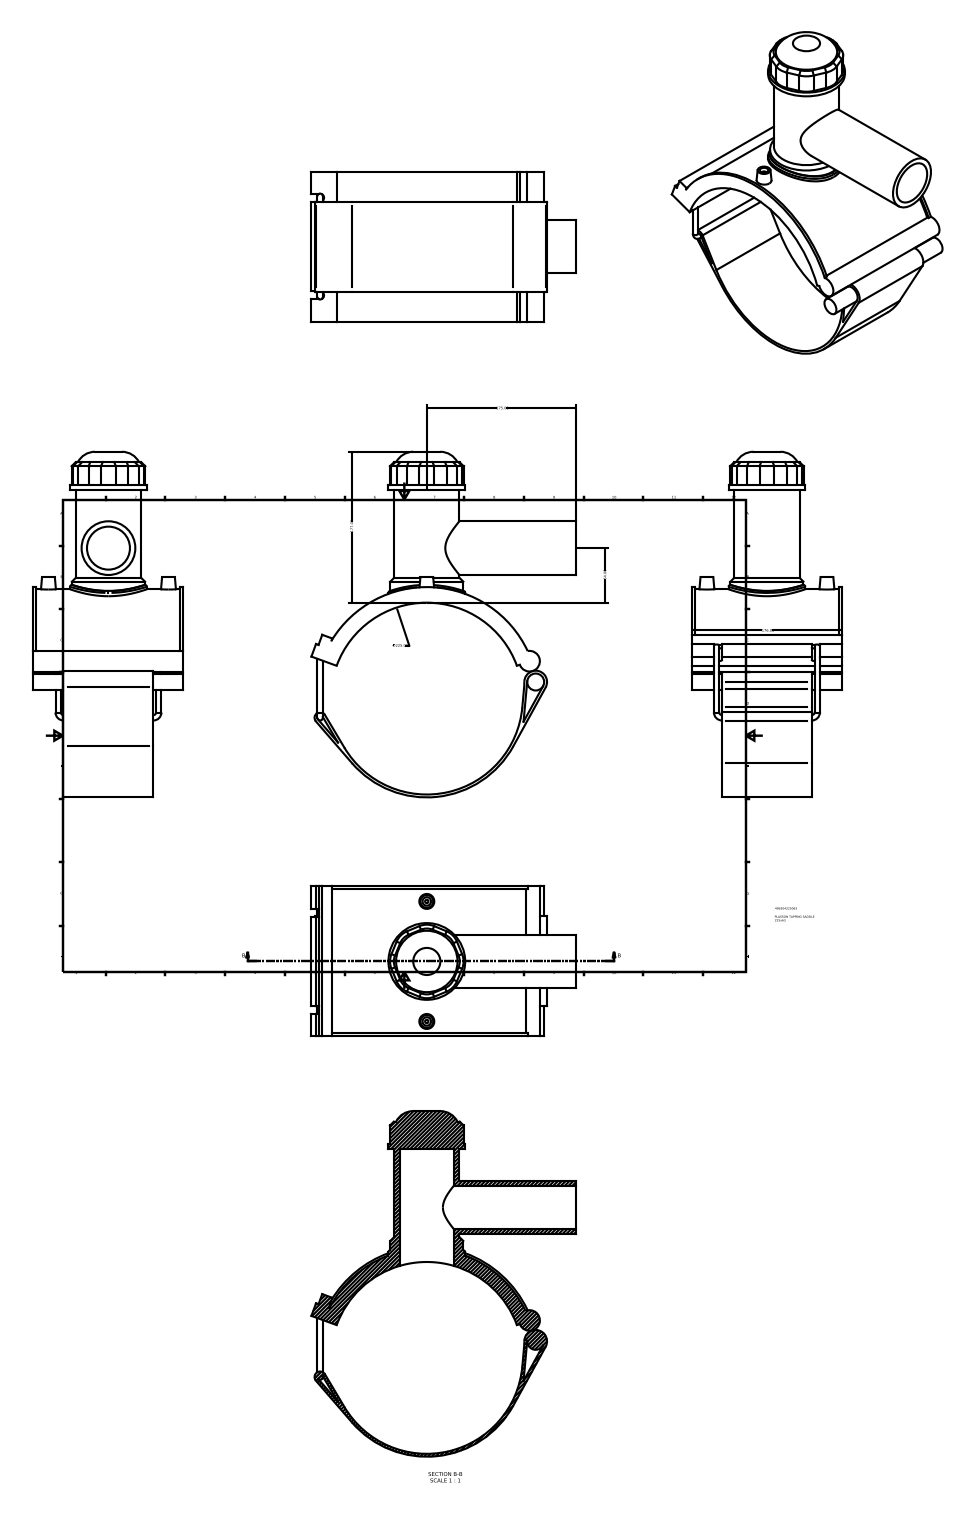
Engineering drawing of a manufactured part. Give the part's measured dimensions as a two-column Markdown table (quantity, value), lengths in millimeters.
| quantity | value |
| --- | --- |
| part name | 496304225063 |
| STEP written by | Autodesk Inventor 2015 (AUTOMOTIVE_DESIGN) |
| units | millimeters |
| bodies | 1 solid, 121 faces (68 planar, 38 cylindrical, 15 other) |
| overall size | 405.38 × 310.32 × 176 |
| volume | 1 714 000 mm³ |
| surface area | 374 360 mm² |
| round holes (diameter × count) | 10 × 2, 50.4 × 1, 63 × 1 |
| round bosses / shafts (diameter × count) | 6.3 × 2, 4 × 2, 90 × 1, 85.5 × 1, 76.5 × 1, 63 × 1, 19.9 × 1 |
| partial cylindrical surfaces (radius × count) | 22.5 × 8, 4.72 × 2, 112.5 × 2, 3.15 × 1, 6.53 × 1, 12.12 × 1, 13.33 × 1, 115.88 × 1 |
| main face-to-face distances | 176, 3.4, 3.38, 3.37, 35.2, 140.8, 3, 3.15, 28.35, 15.76 |
| hole center spacings | 70.4, 140.8 |
